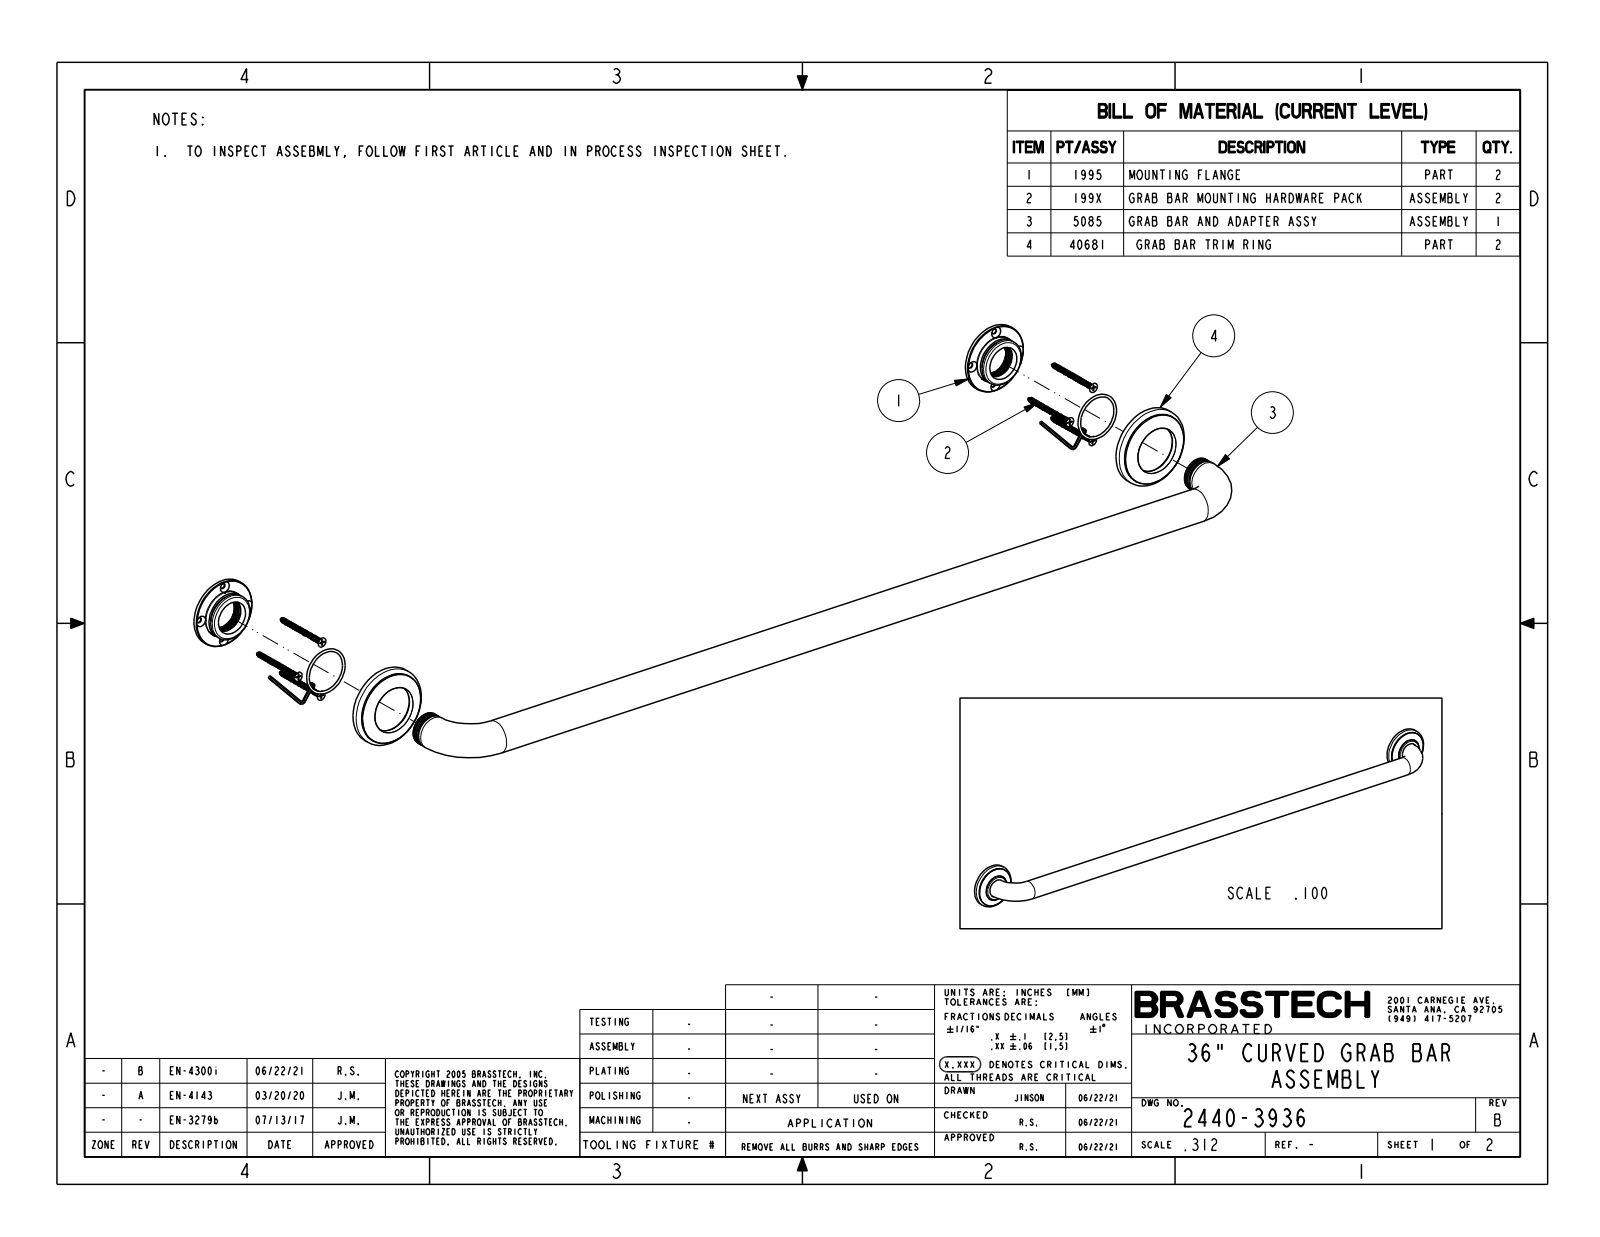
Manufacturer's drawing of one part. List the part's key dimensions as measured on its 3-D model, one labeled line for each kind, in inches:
Part name (STEP PRODUCT): 2440-3936
STEP written by: CREO PARAMETRIC BY PTC INC, 2018400 (CONFIG_CONTROL_DESIGN)
Units: inches
Bodies: 1 solid, 48 faces (6 planar, 14 cylindrical, 28 other)
Overall size (bounding box): 39 × 3 × 2.75
Volume: 52.78 in³ · Surface area: 180.6 in²
Round bosses / shafts (diameter × count): ⌀3 ×2, ⌀2.72 ×2, ⌀1.75 ×2, ⌀1.25 ×1
Main face-to-face distances: 0.6, 0.519, 0.081
